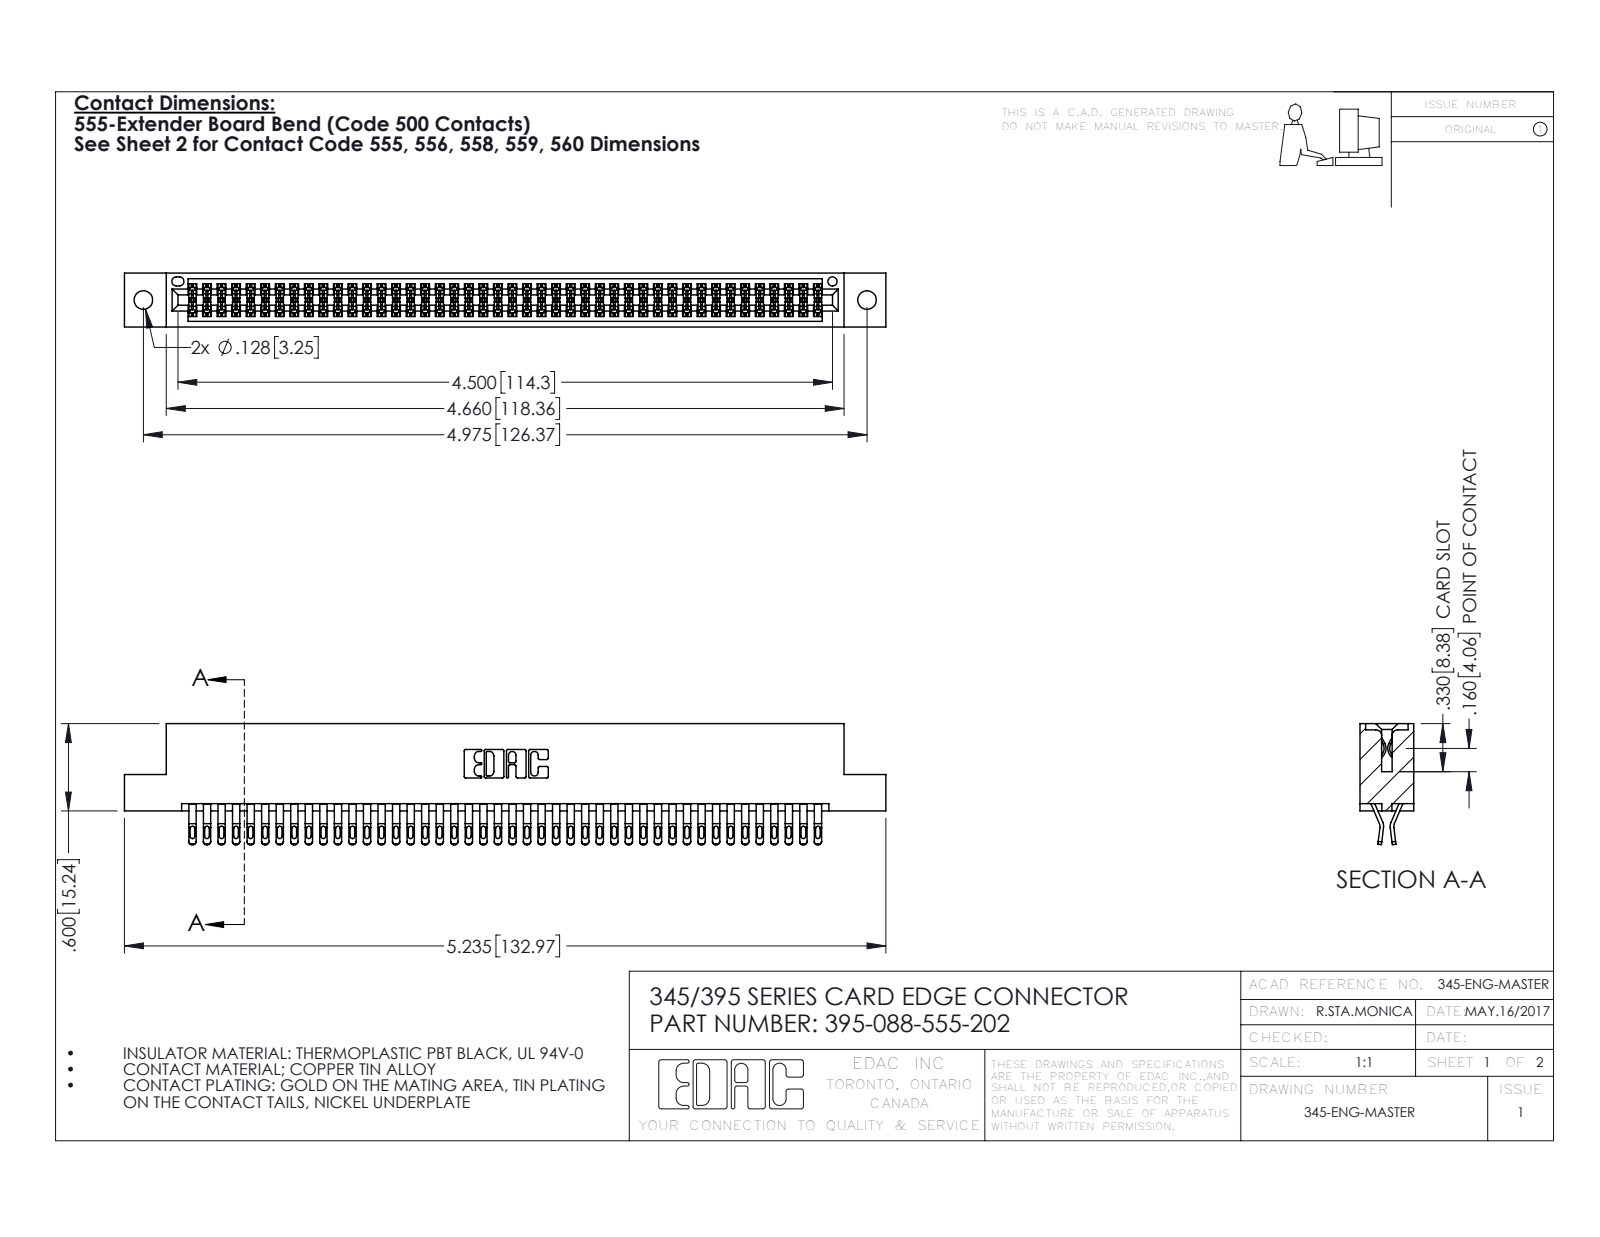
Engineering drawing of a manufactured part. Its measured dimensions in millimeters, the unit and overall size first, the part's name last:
Units: millimetres
Overall size (bounding box): 133 × 21.1 × 9.4
Round holes (diameter × count): ⌀3.3 ×2, ⌀1.6 ×1
Partial cylindrical surfaces — rounded edges, fillets, slot ends (radius × count): R0.4 ×220, R0.5 ×176, R0.2 ×132, R0.3 ×22, R0.2 ×6, R0.8 ×6, R0.7 ×3, R0.3 ×2
Main face-to-face distances: 7.6, 1.8, 0.6, 9.4, 5.1, 2.5, 6.9, 5.7, 4.4, 3.8
Hole centre spacings: 6.9, 120.4, 126.4
Volume: 13 200 mm³ · Surface area: 20 100 mm²
Bodies: 89 solids, 5054 faces (2808 planar, 2246 cylindrical, 0 other)
Part name (STEP PRODUCT): 345 Part_Flush Mounting Lugs - 0.128 Dia; 395-088-555-202; 345-292-001_555 Tail
STEP written by: SolidWorks 2016 (CONFIG_CONTROL_DESIGN)
